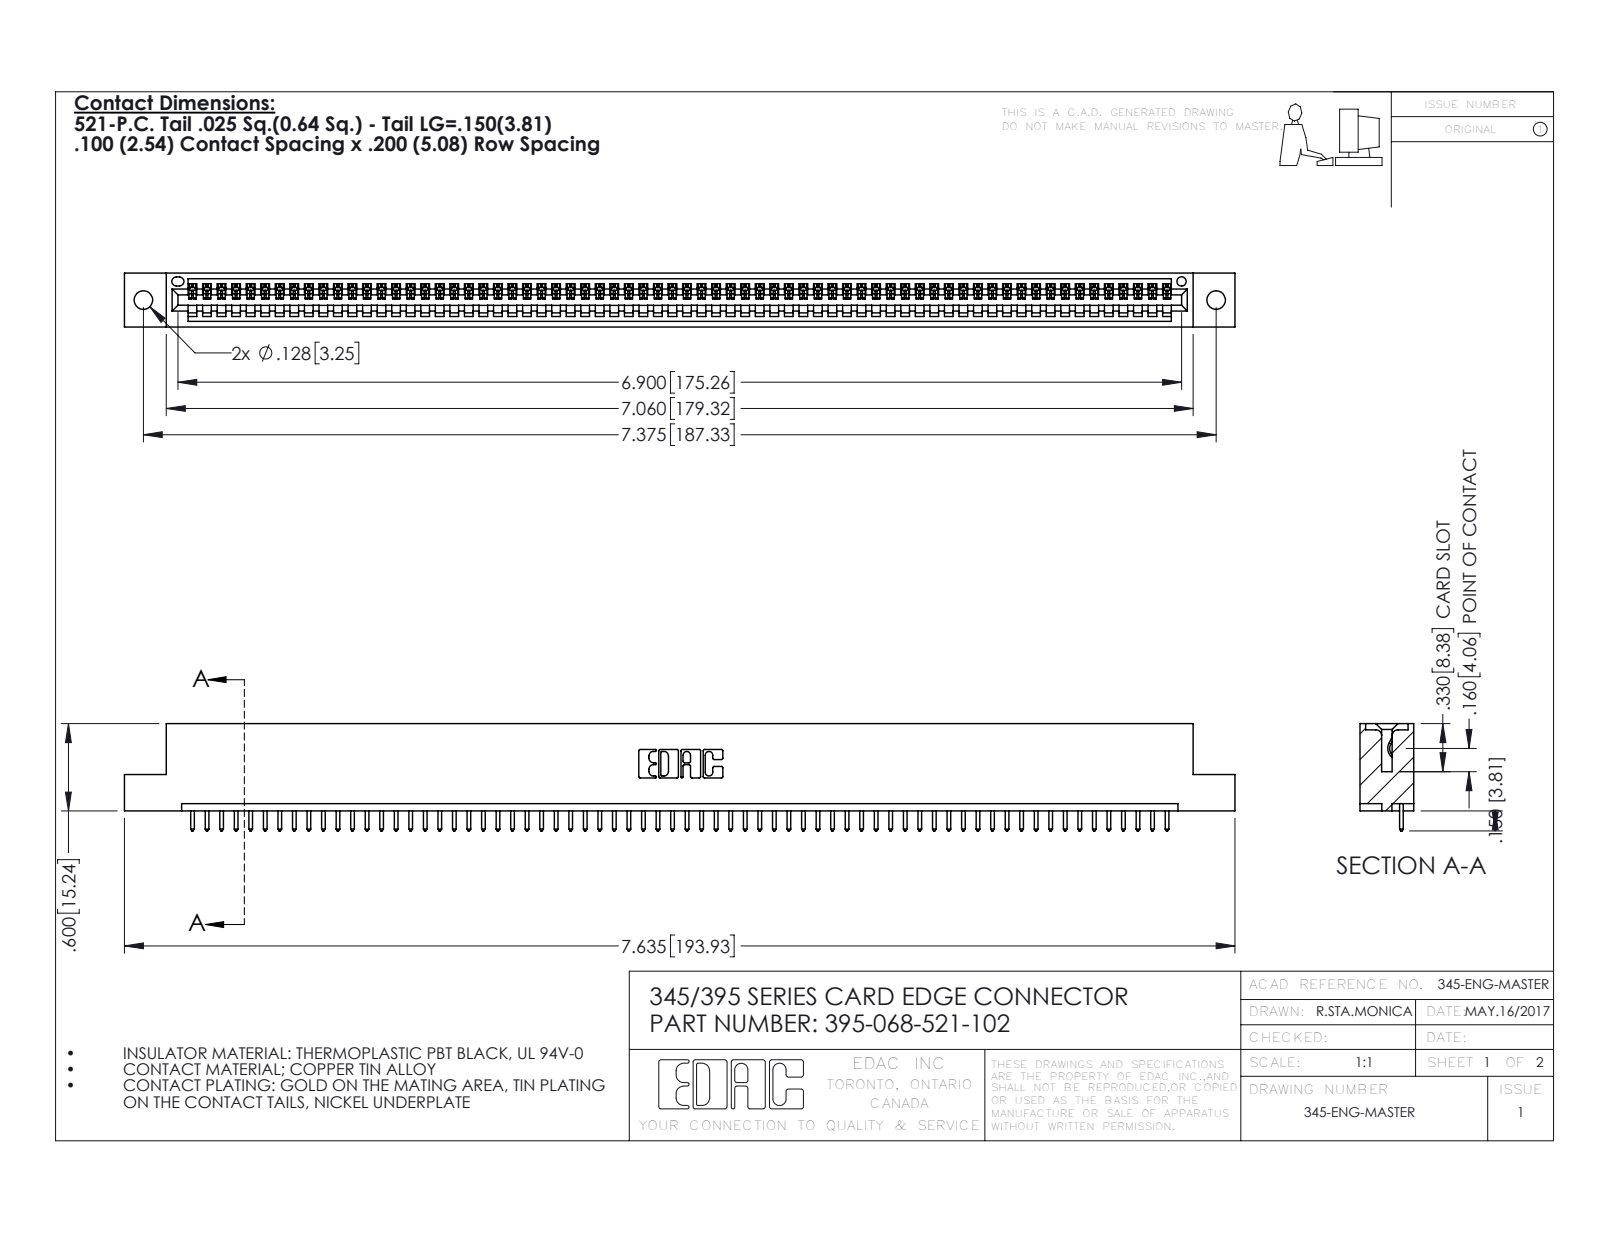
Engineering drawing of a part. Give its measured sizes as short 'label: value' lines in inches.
name: 345-292-001_345-293-121; 395-068-521-102; 345 Part_Flush Mounting Lugs - 0.128 Dia
written by: SolidWorks 2016 (CONFIG_CONTROL_DESIGN)
unit: in
bodies: 69 solids, 4070 faces (2800 planar, 1270 cylindrical, 0 other)
size: 7.635 × 0.737 × 0.37
volume: 1.123 in³; area: 36.86 in²
holes: 2× ⌀0.128, 1× ⌀0.064
rounds: 136× R0.006, 136× R0.01, 22× R0.01, 6× R0.007, 6× R0.031, 3× R0.026, 2× R0.031, 2× R0.04
face distances: 0.298, 0.072, 0.37, 0.2, 0.098, 0.272, 0.025, 0.225, 0.149, 0.072
hole spacings: 0.27, 7.139, 7.375
